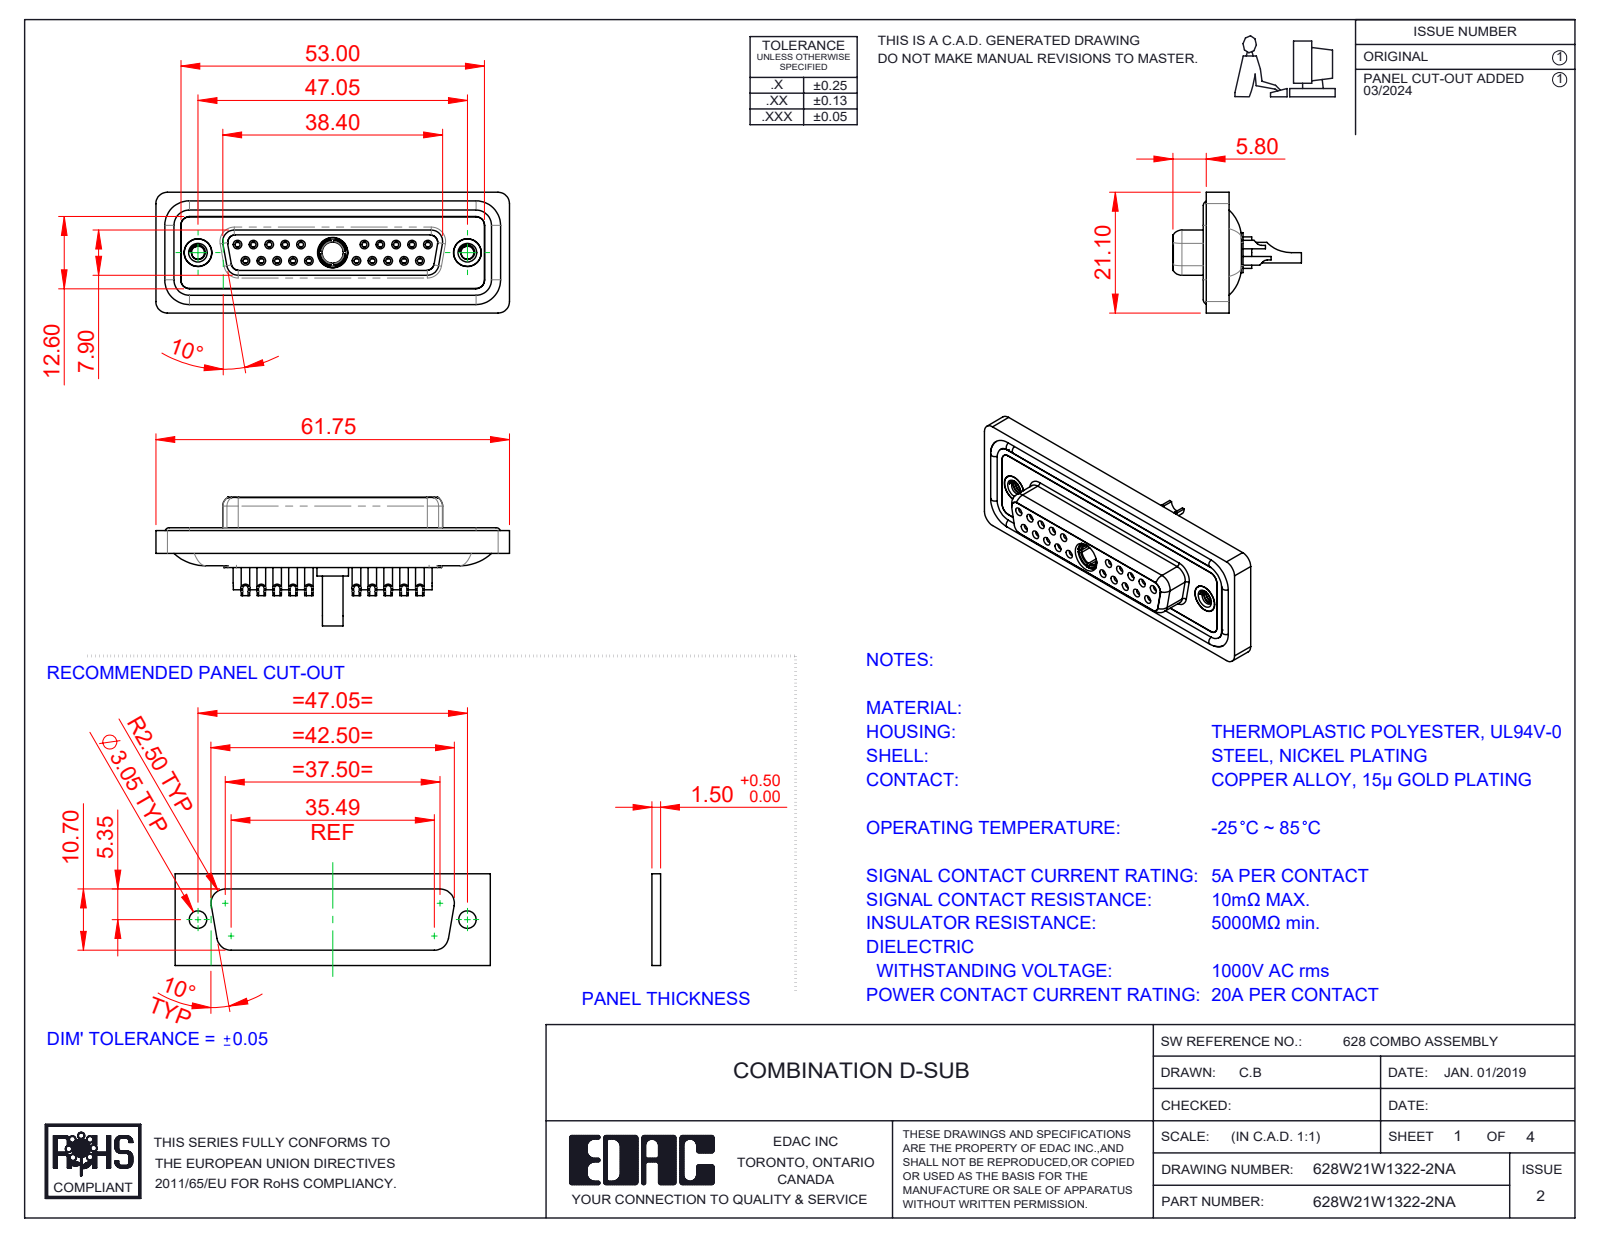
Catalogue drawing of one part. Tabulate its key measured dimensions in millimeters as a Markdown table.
| quantity | value |
| --- | --- |
| part name | 628W21W1322-2NA; Power Socket_20A SC; 628Combo Shell Front_25 Contacts; 628Combo Shell Rear_25 Contacts (+5 more) |
| STEP written by | SolidWorks 2023 (CONFIG_CONTROL_DESIGN) |
| units | millimeters |
| bodies | 29 solids, 1564 faces (477 planar, 636 cylindrical, 451 other) |
| overall size | 61.75 × 22.45 × 21.1 |
| volume | 8 429 mm³ |
| surface area | 14 292 mm² |
| round holes (diameter × count) | 0.9 × 20, 1 × 20, 1.1 × 20, 1.5 × 20, 2 × 20, 1.6 × 10, 1.7 × 10, 4.85 × 3, 2.26 × 2, 4 × 2, 4.05 × 2, 5 × 2 |
| round bosses / shafts (diameter × count) | 2.2 × 20, 1.6 × 14, 4.95 × 2, 4.8 × 2, 5.5 × 1, 5.2 × 1, 4.96 × 1, 4.75 × 1 |
| partial cylindrical surfaces (radius × count) | 1.5 × 22, 2 × 18, 1.35 × 8, 1.6 × 8, 1 × 6, 0.25 × 4, 0.5 × 4, 0.6 × 4 |
| main face-to-face distances | 0.4, 1.8, 7.45, 5.65, 6.6, 0.5, 1.6, 7.05, 2.9, 1.1 |
| hole center spacings | 3.16, 2.77, 5.54, 5.03, 8.31, 7.48, 16.62, 19.39 |
